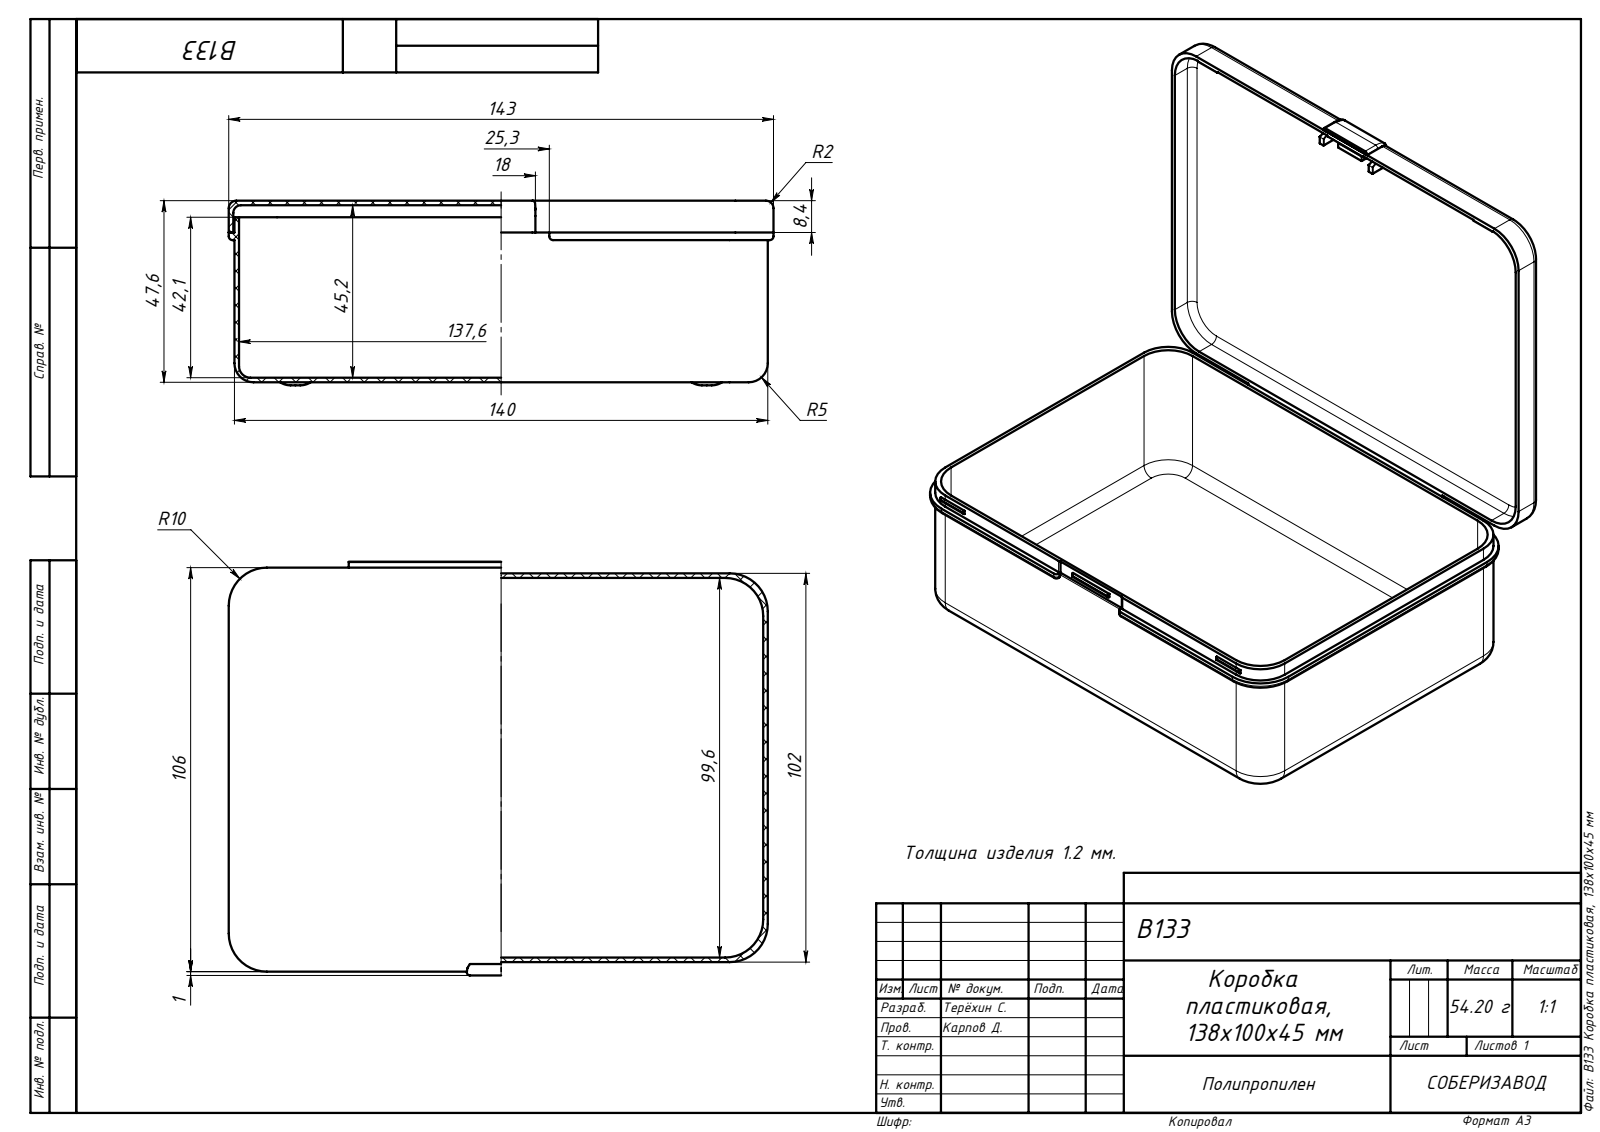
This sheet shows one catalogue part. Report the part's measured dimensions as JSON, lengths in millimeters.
{"part_name": "B133 Коробка пластиковая, 138x100x45 мм; B133 Емкость_00; B133 Крышка_00", "step_written_by": "SolidWorks 2019 (AUTOMOTIVE_DESIGN)", "units": "millimeters", "bodies": {"solids": 3, "faces": 241, "planar": 89, "cylindrical": 100, "other": 52}, "overall_size": [143, 108.5, 48.45], "volume_mm3": 63741, "surface_area_mm2": 105192, "partial_cylinders_radius": [[0.2, 19], [10, 16], [0.4, 15], [1, 11], [2, 8], [0.8, 4], [3, 4], [5, 4]], "face_to_face_distances": [1.2, 46.45, 45.25, 47.65, 100.8, 138.8, 99.6, 102, 1.5, 137.6]}
